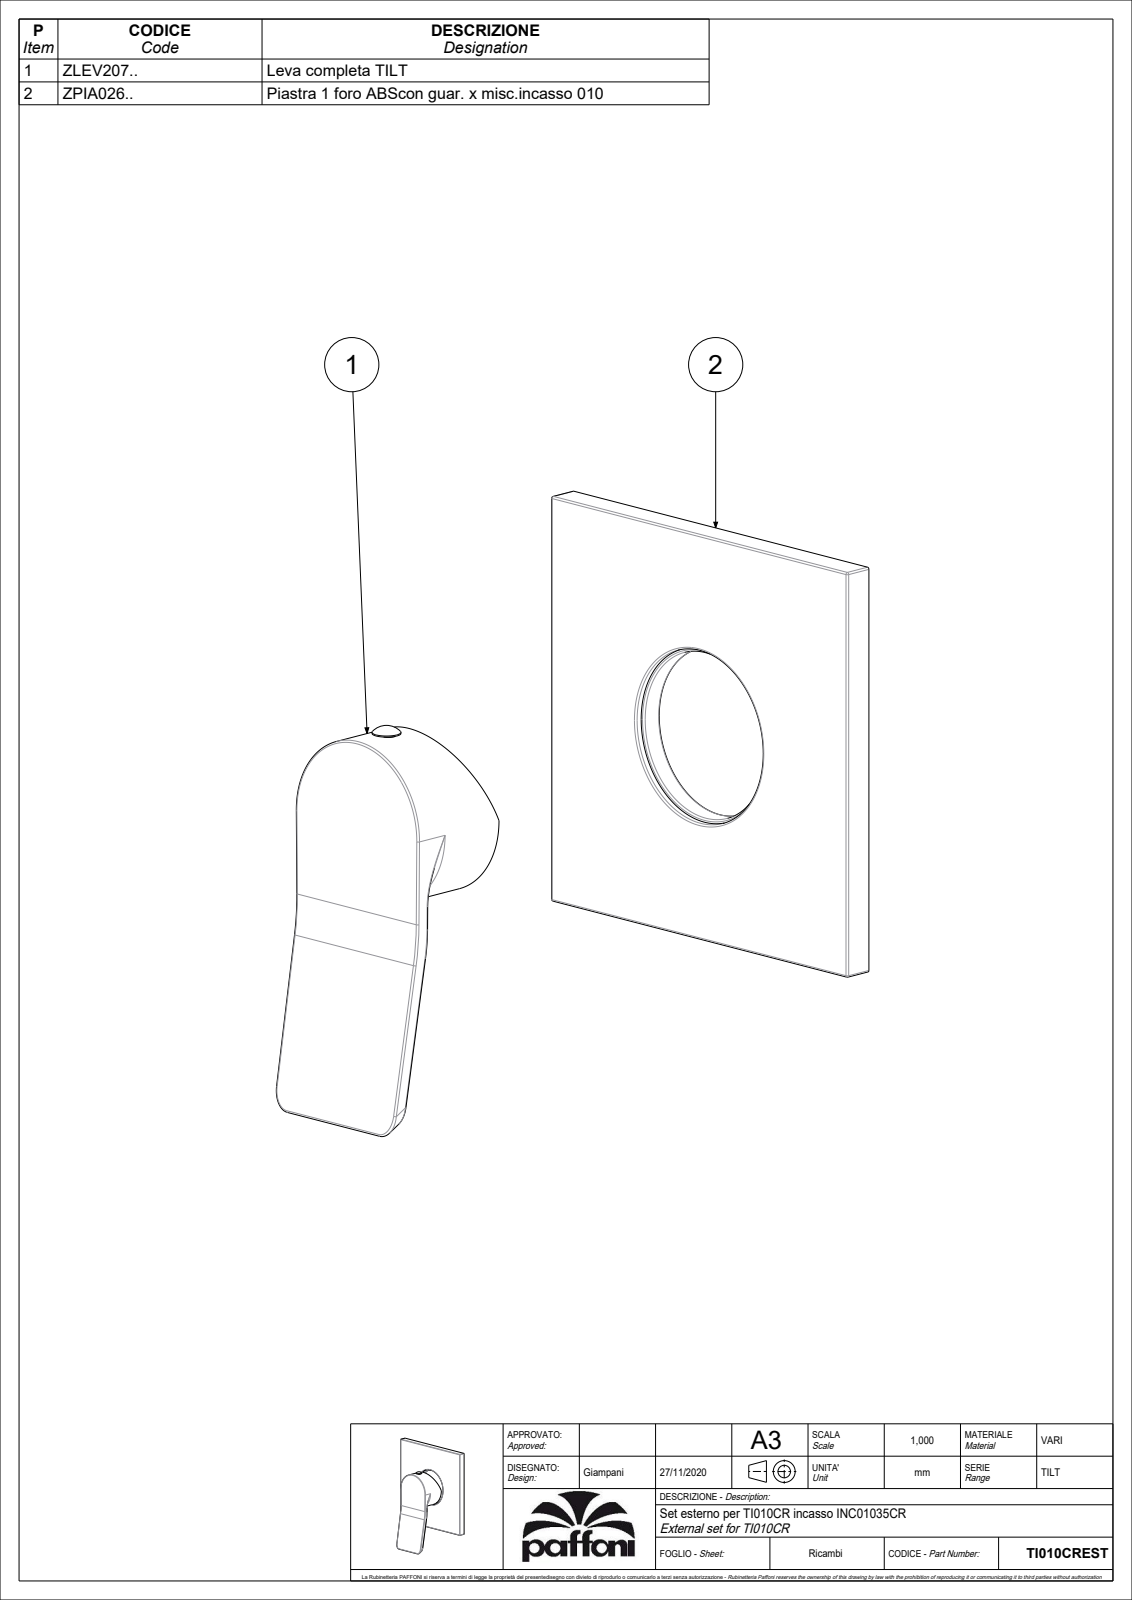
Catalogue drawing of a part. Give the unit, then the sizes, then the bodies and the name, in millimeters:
Units: millimetres
Overall size (bounding box): 134.58 × 110 × 48.95
Round holes (diameter × count): ⌀3 ×1, ⌀45 ×1, ⌀47 ×1, ⌀49 ×1
Round bosses / shafts (diameter × count): ⌀51 ×1, ⌀45.5 ×1, ⌀7.6 ×1, ⌀5.5 ×1, ⌀5 ×1
Partial cylindrical surfaces — rounded edges, fillets, slot ends (radius × count): R0.5 ×26, R1 ×4, R2 ×4, R1.5 ×2, R5 ×2, R44.14 ×1, R63 ×1
Main face-to-face distances: 7, 2, 5, 108, 2.5, 0.5, 107.5, 105.5, 4.01, 32
Volume: 86 935 mm³ · Surface area: 50 566 mm²
Bodies: 2 solids, 197 faces (74 planar, 70 cylindrical, 53 other)
Part name (STEP PRODUCT): TI010CREST
STEP written by: CREO PARAMETRIC BY PTC INC, 2020044 (CONFIG_CONTROL_DESIGN)
